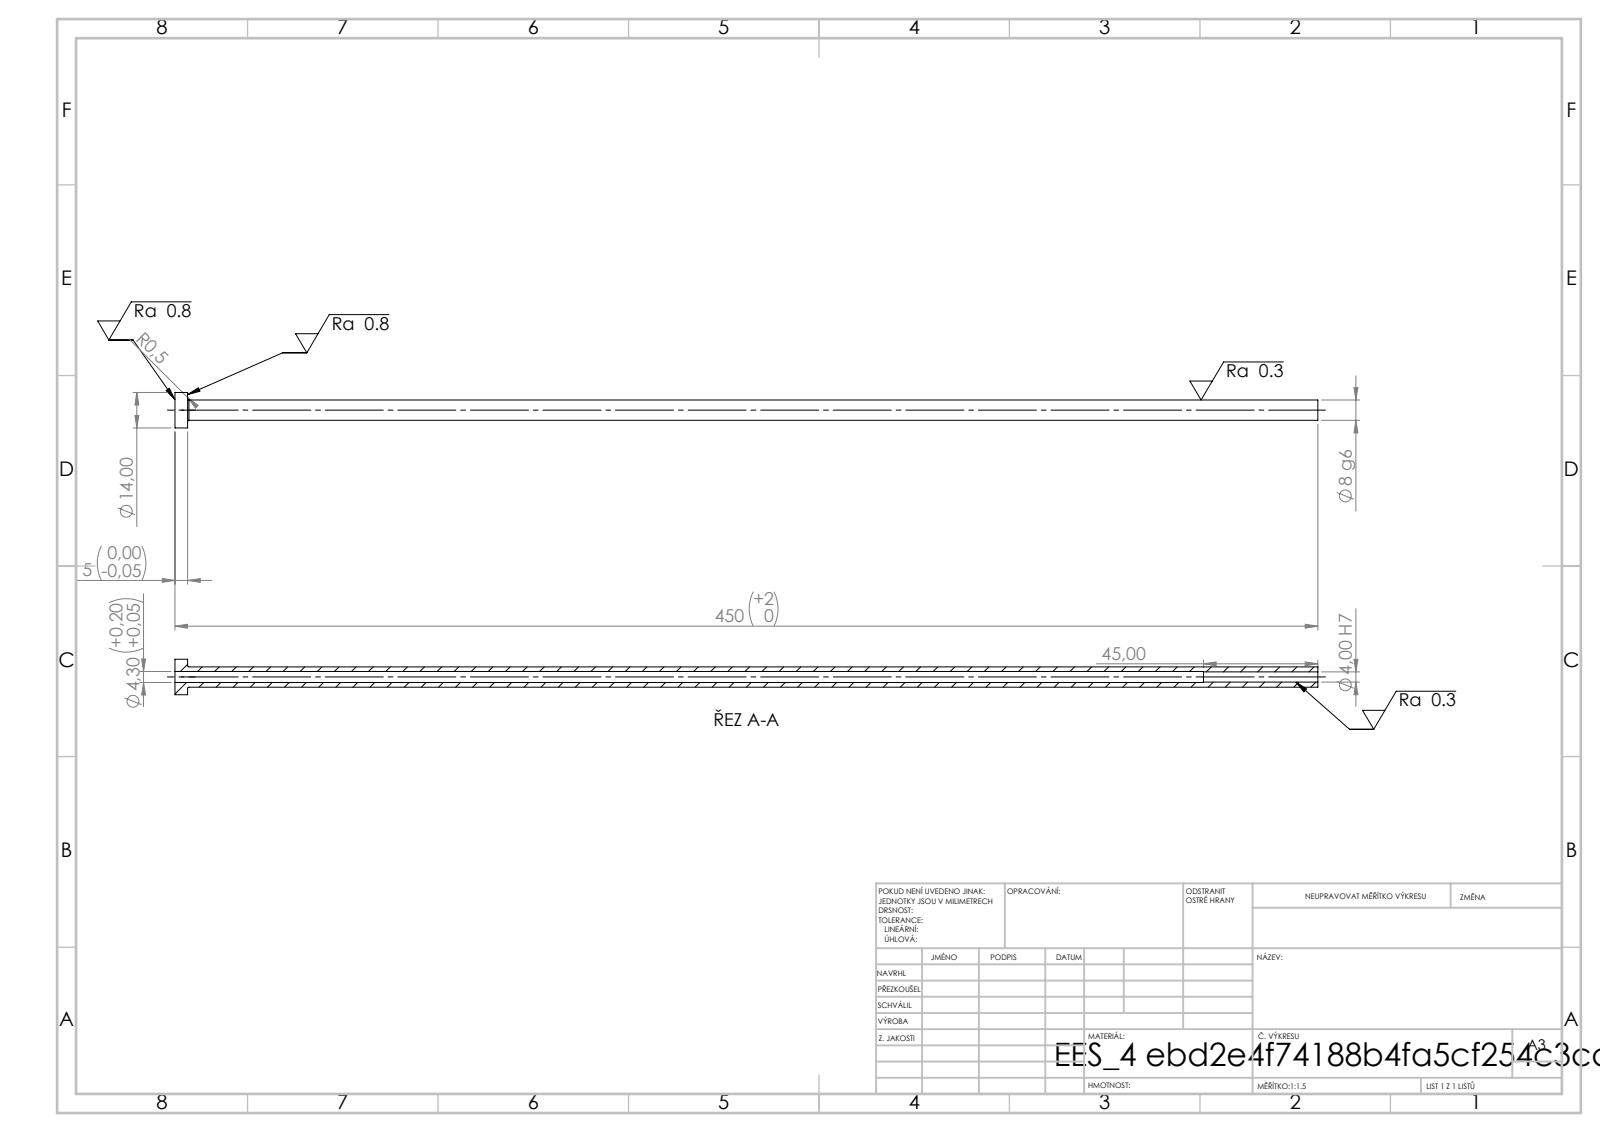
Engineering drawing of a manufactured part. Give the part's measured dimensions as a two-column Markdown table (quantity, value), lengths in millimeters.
| quantity | value |
| --- | --- |
| STEP written by | SolidWorks 2019 (CONFIG_CONTROL_DESIGN) |
| units | millimeters |
| bodies | 1 solid, 14 faces (4 planar, 8 cylindrical, 2 other) |
| overall size | 450 × 14 × 14 |
| volume | 16 692 mm³ |
| surface area | 17 718 mm² |
| round holes (diameter × count) | 4 × 1, 4.3 × 1 |
| round bosses / shafts (diameter × count) | 14 × 1, 8 × 1 |
| main face-to-face distances | 5, 450, 445, 405, 400, 45 |
